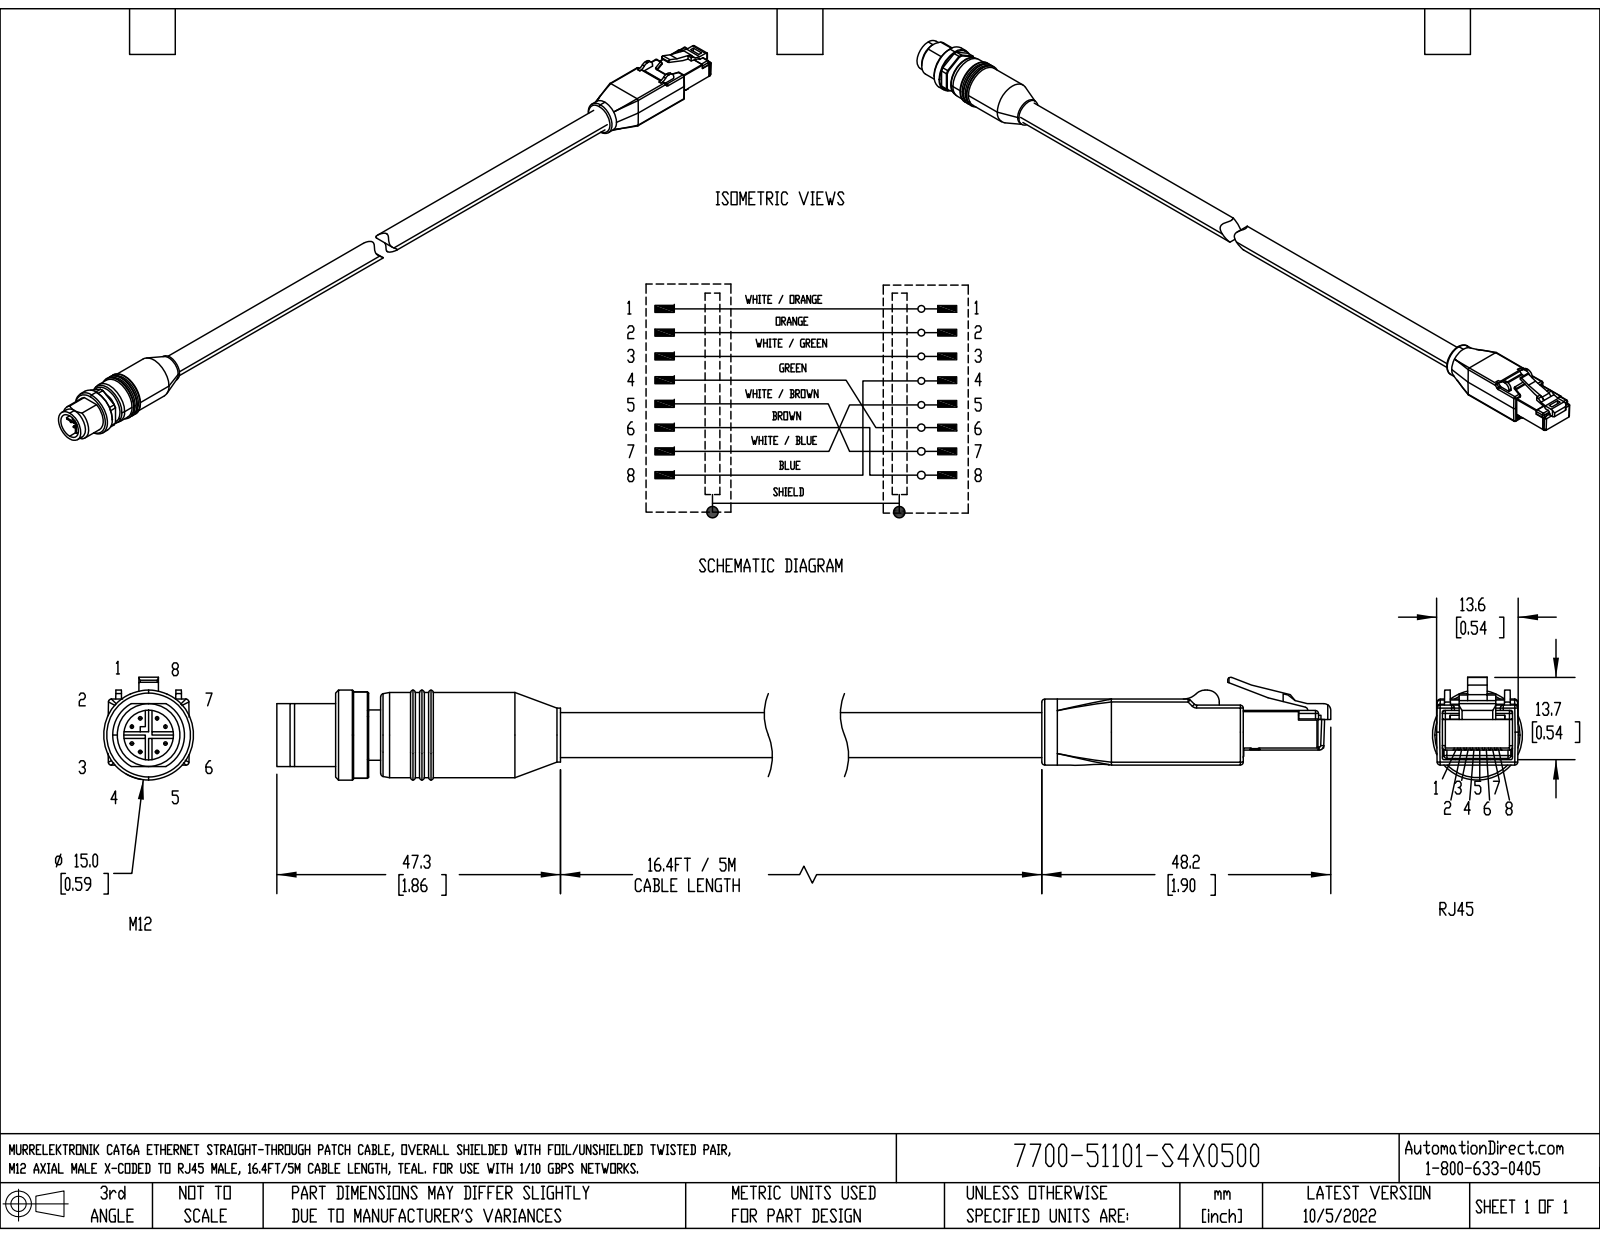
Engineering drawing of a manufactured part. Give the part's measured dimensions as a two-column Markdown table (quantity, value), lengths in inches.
| quantity | value |
| --- | --- |
| part name | 7700-51101-S4X0500 |
| STEP written by | SolidWorks 2021 (AUTOMOTIVE_DESIGN) |
| units | inches |
| bodies | 4 solids, 535 faces (291 planar, 155 cylindrical, 89 other) |
| overall size | 11.73 × 0.675 × 0.591 |
| volume | 1.403 in³ |
| surface area | 21.44 in² |
| round holes (diameter × count) | 0.327 × 1 |
| round bosses / shafts (diameter × count) | 0.024 × 8, 0.591 × 1, 0.559 × 1, 0.433 × 1, 0.413 × 1, 0.354 × 1, 0.331 × 1, 0.295 × 1 |
| partial cylindrical surfaces (radius × count) | 0.02 × 46, 0.008 × 15, 0.012 × 6, 0.006 × 2, 0.079 × 2, 0.197 × 2, 0.03 × 1, 0.039 × 1 |
| main face-to-face distances | 0.358, 0.035, 0.452, 0.35, 0.535, 0.46, 0.45, 0.442, 0.085, 0.075 |
